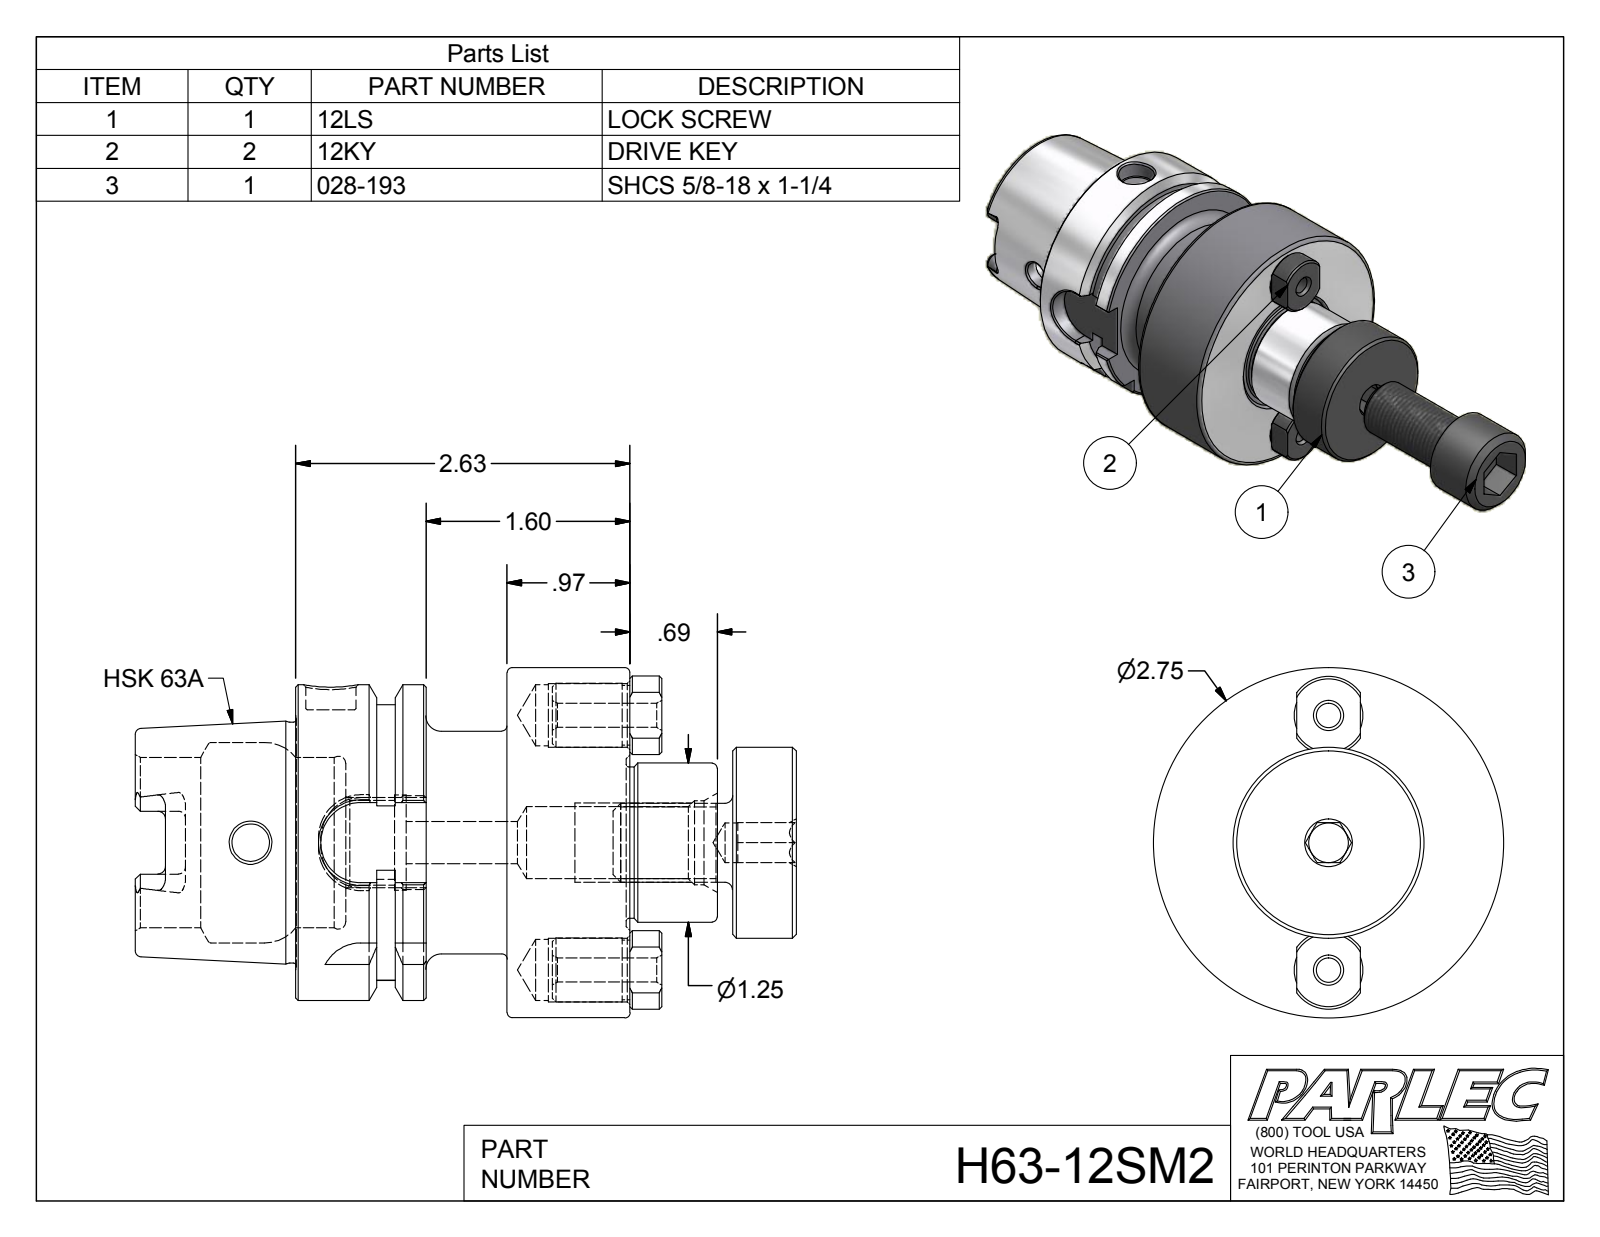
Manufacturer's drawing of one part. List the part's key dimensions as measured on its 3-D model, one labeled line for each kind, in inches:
Part name (STEP PRODUCT): H63-12SM2; H63-12SM2-1; 12KY; 12LS (+1 more)
STEP written by: Autodesk Inventor 2012 (AUTOMOTIVE_DESIGN)
Units: inches
Bodies: 5 solids, 226 faces (88 planar, 57 cylindrical, 81 other)
Overall size (bounding box): 7.192 × 2.75 × 2.75
Volume: 14.43 in³ · Surface area: 80.52 in²
Round holes (diameter × count): ⌀0.19 ×2, ⌀0.48 ×2, ⌀0.5 ×2, ⌀0.295 ×1, ⌀0.312 ×1, ⌀0.331 ×1, ⌀0.394 ×1, ⌀0.565 ×1, ⌀0.66 ×1, ⌀0.666 ×1, ⌀0.749 ×1, ⌀1.339 ×1
Round bosses / shafts (diameter × count): ⌀0.505 ×2, ⌀0.47 ×2, ⌀2.75 ×1, ⌀2.48 ×1, ⌀1.891 ×1, ⌀1.75 ×1, ⌀1.5 ×1, ⌀1.25 ×1
Partial cylindrical surfaces — rounded edges, fillets, slot ends (radius × count): R0.059 ×6, R0.113 ×4, R0.315 ×4, R0.308 ×2, R1.083 ×1
Main face-to-face distances: 0.965, 1.66, 2.625, 3.932, 2.272, 1.307, 0.5, 1.024, 0.636, 1.602
Hole centre spacings: 1, 2
